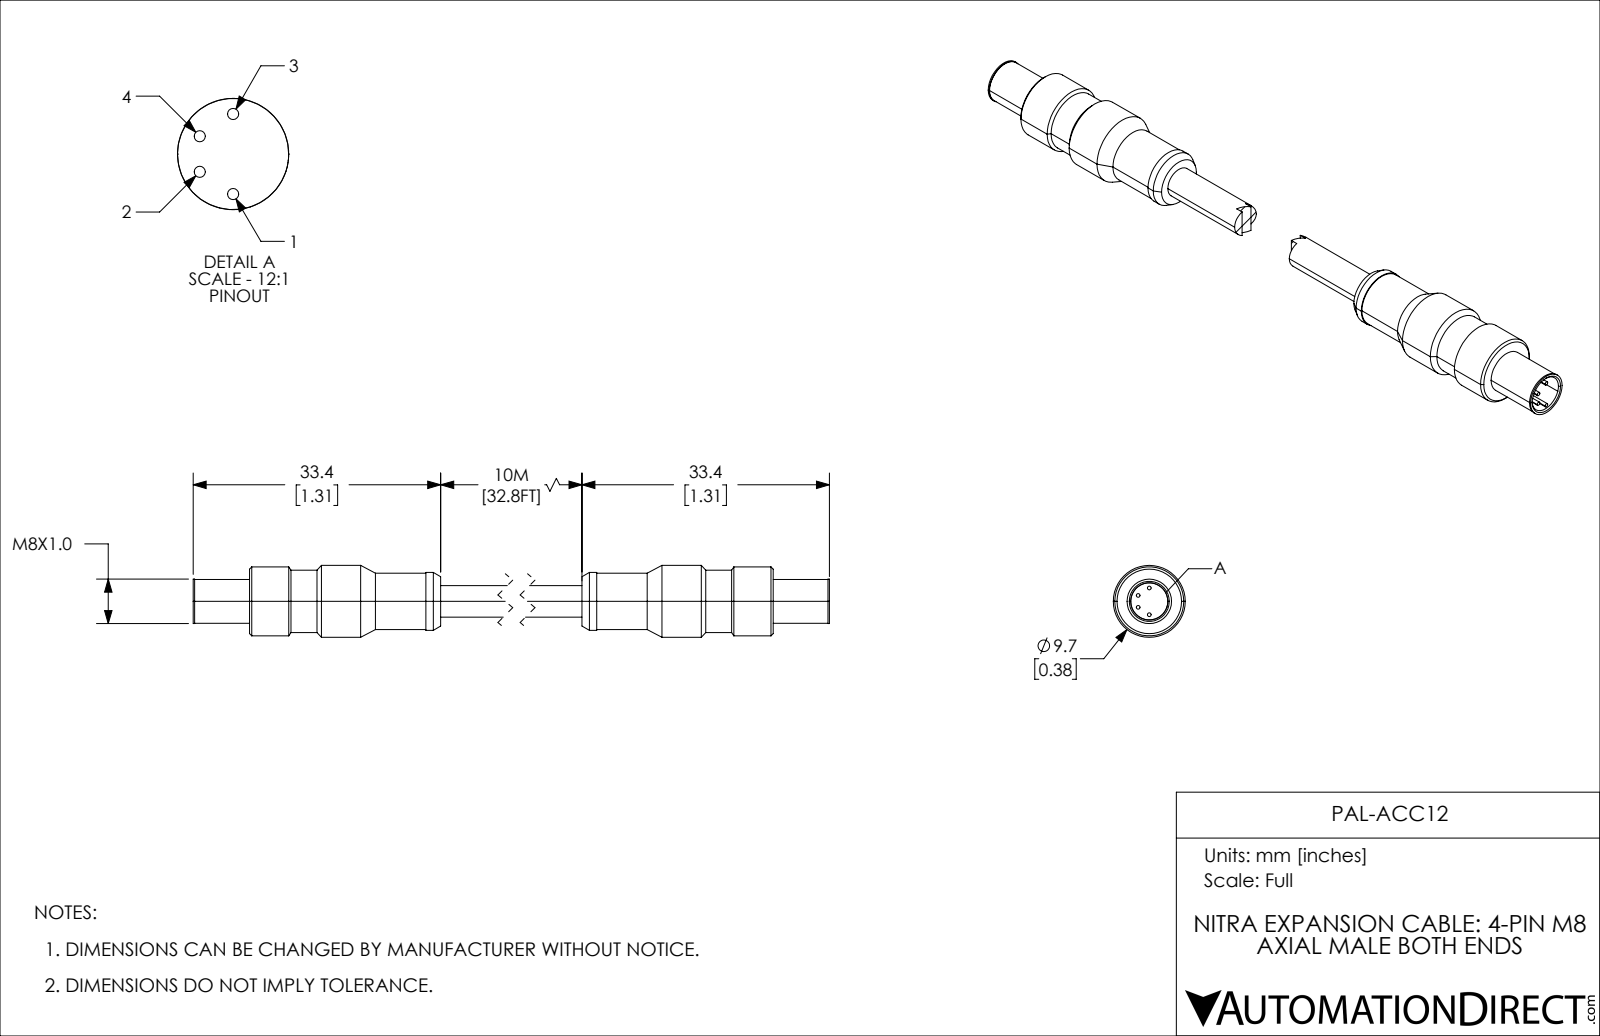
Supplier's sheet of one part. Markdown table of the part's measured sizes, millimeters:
| quantity | value |
| --- | --- |
| part name | PAL-ACC12 |
| STEP written by | SolidWorks 2019 (CONFIG_CONTROL_DESIGN) |
| units | millimeters |
| bodies | 1 solid, 99 faces (20 planar, 52 cylindrical, 27 other) |
| overall size | 62.62 × 23.89 × 9.7 |
| volume | 4 144 mm³ |
| surface area | 2 952 mm² |
| round holes (diameter × count) | 5 × 2 |
| round bosses / shafts (diameter × count) | 0.5 × 8, 9.7 × 2, 9.3 × 2, 8.4 × 2, 7.8 × 2, 7.6 × 2, 6 × 2, 5.9 × 2 |
| main face-to-face distances | 25.8, 2.6, 28.4, 5, 7.6, 33.4, 31.4, 26.4, 23.8, 2 |
| hole center spacings | 14.19 |
